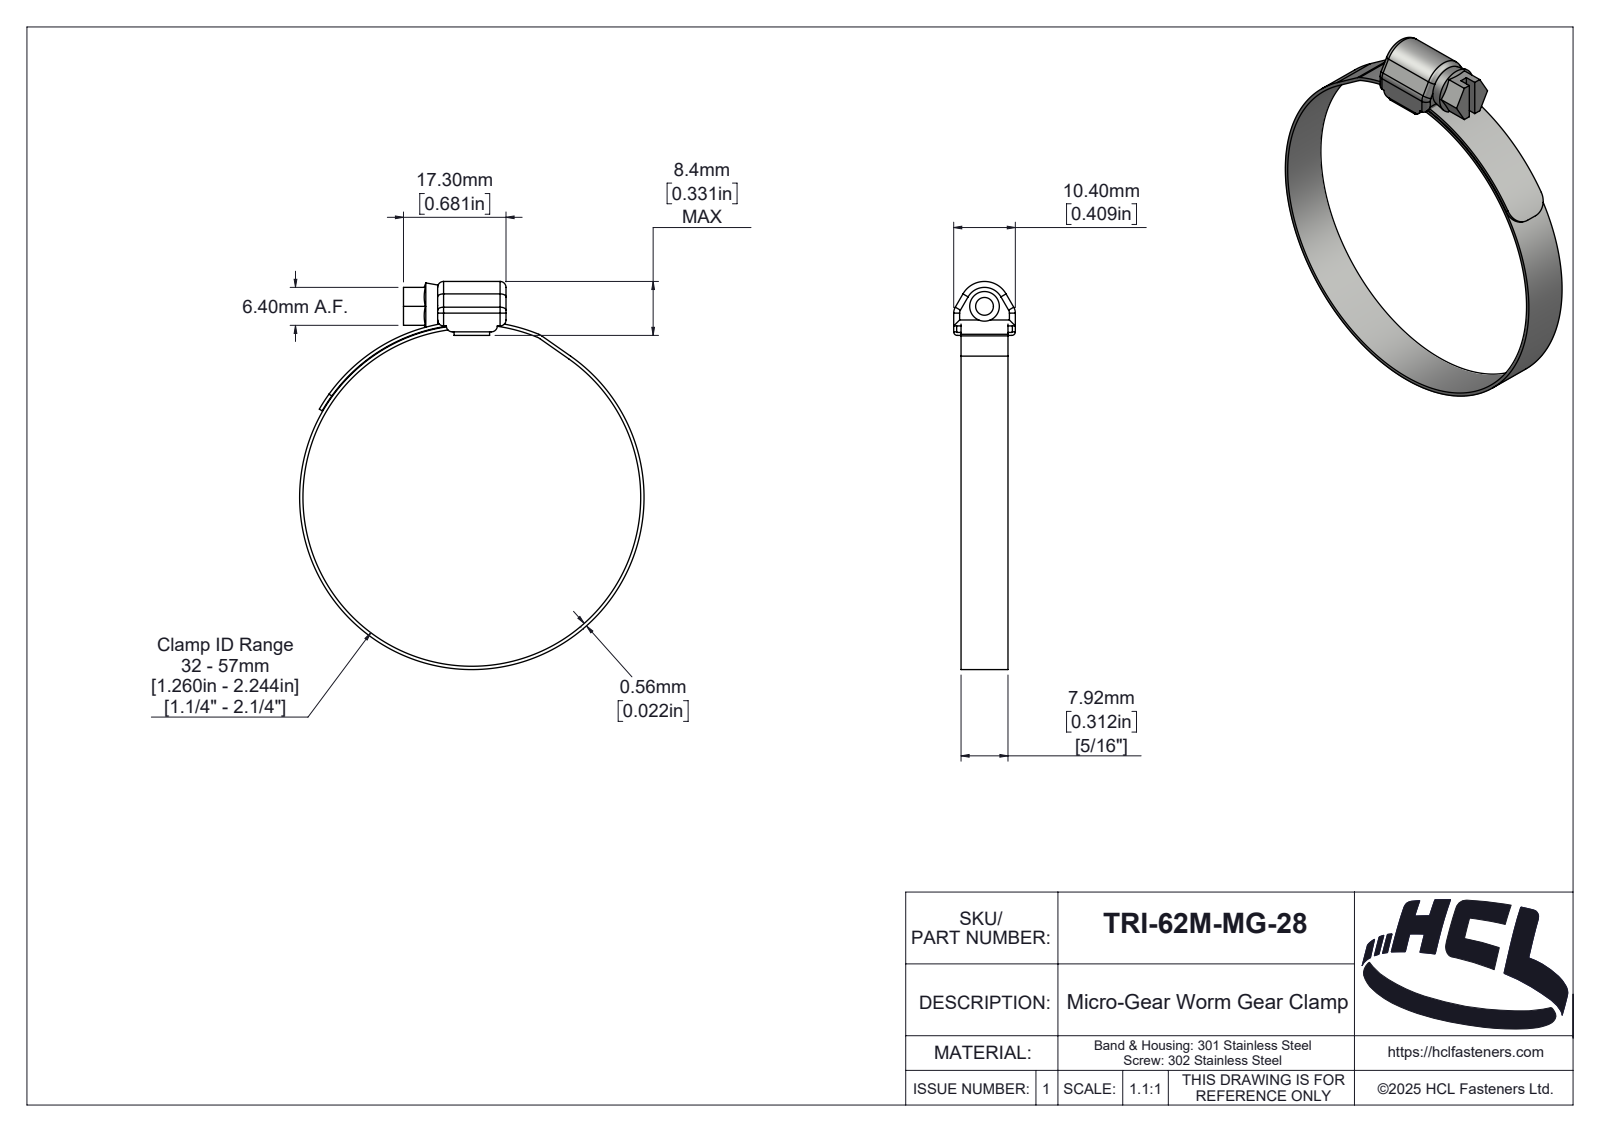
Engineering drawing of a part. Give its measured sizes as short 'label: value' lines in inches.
name: TRI-62M-MG-28
written by: SolidWorks 2025 (AUTOMOTIVE_DESIGN)
unit: in
bodies: 3 solids, 186 faces (38 planar, 87 cylindrical, 61 other)
size: 2.577 × 2.288 × 0.409
volume: 0.115 in³; area: 7.381 in²
holes: 1× ⌀0.197, 1× ⌀2.244
bosses: 1× ⌀2.288
rounds: 12× R0.039, 3× R0.079, 2× R0.004, 2× R0.024, 2× R0.118, 1× R0.01, 1× R0.04, 1× R0.05
face distances: 0.312, 0.043, 0.02, 0.049, 0.361, 0.063, 0.022, 0.244, 0.409, 0.227
